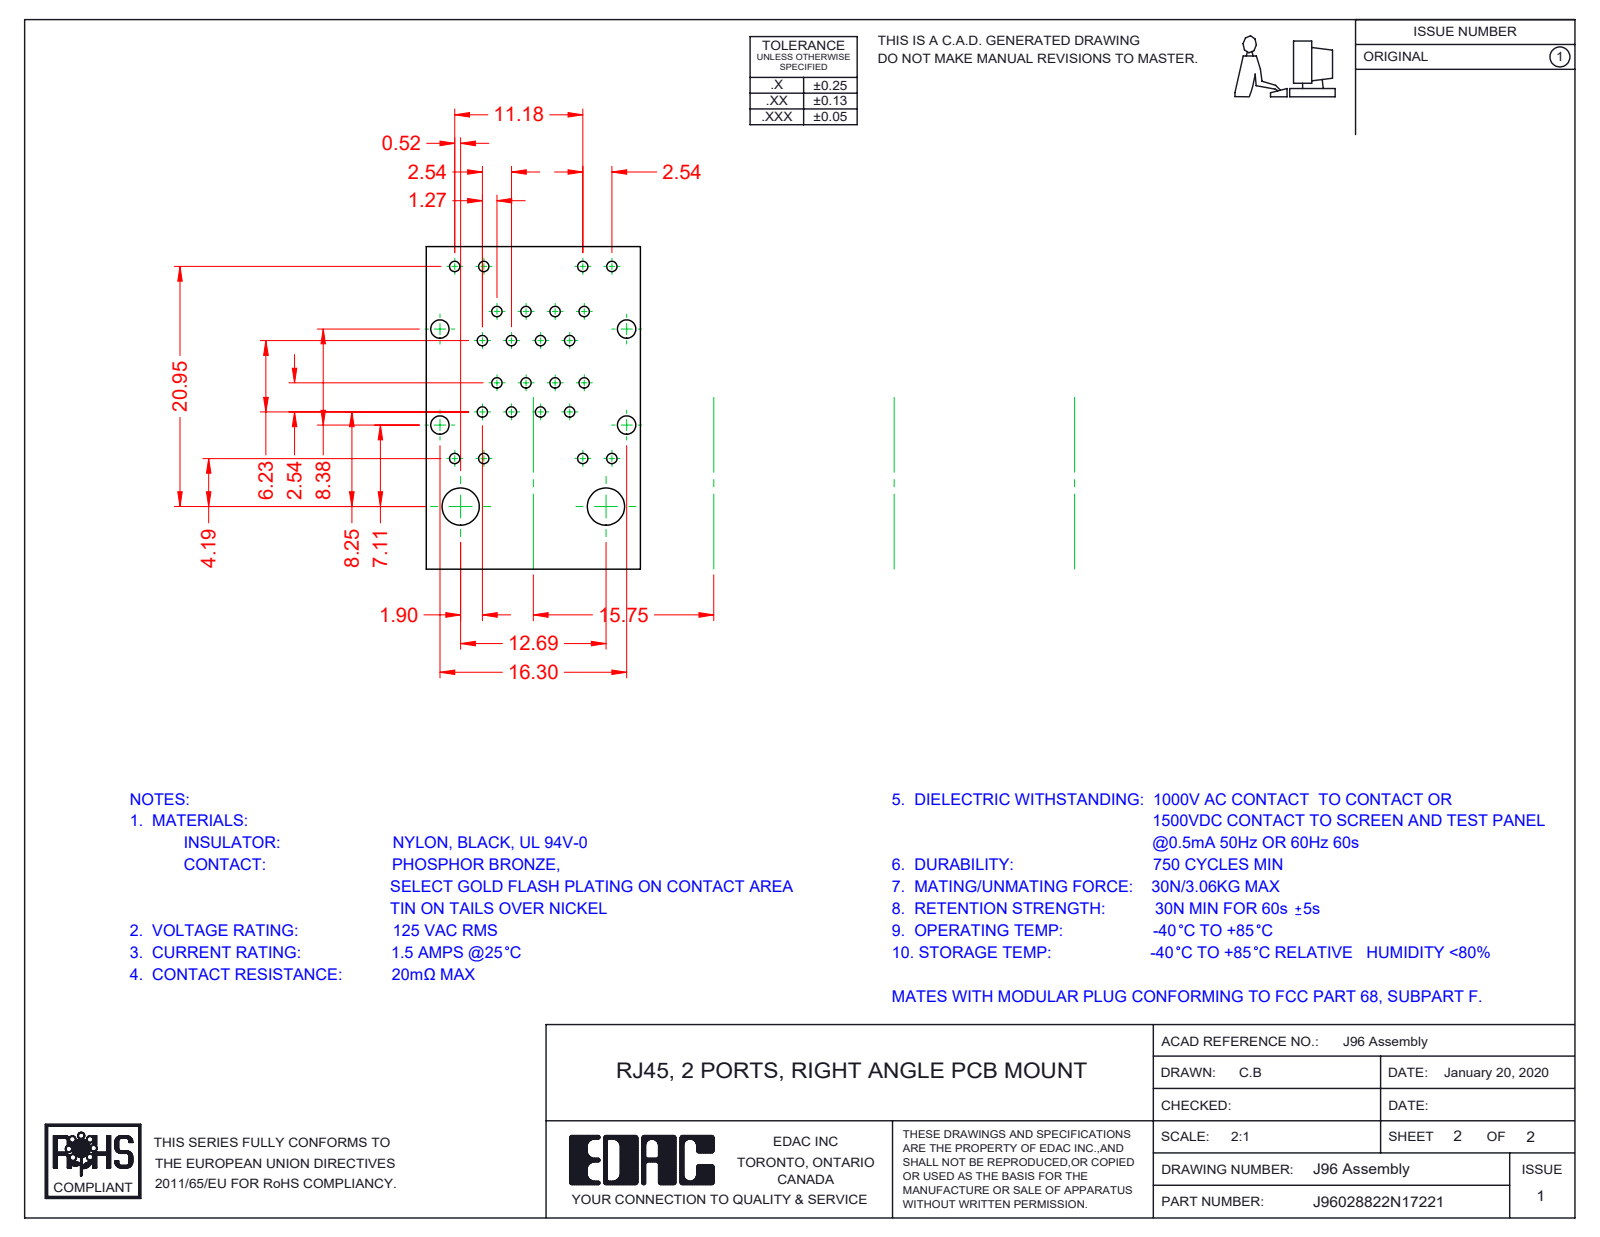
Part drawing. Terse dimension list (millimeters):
name: 96 Contact Lock Lower; 96 Contacts Upper; 96 LED RH Lower_7-Green-Orange; 96 LED RH Upper_7-Green-Orange (+8 more)
written by: SolidWorks 2016 (CONFIG_CONTROL_DESIGN)
unit: mm
bodies: 27 solids, 2421 faces (1865 planar, 450 cylindrical, 106 other)
size: 31.38 × 28.68 × 16.8
volume: 6 849 mm³; area: 19 094 mm²
rounds: 48× R0.25, 32× R0.15, 24× R0.35, 16× R0.5, 16× R1, 14× R0.2, 9× R0.7, 5× R2
face distances: 16.3, 16.1, 1.75, 16.5, 14.75, 1.55, 14.55, 0.53, 1.48, 11.2
